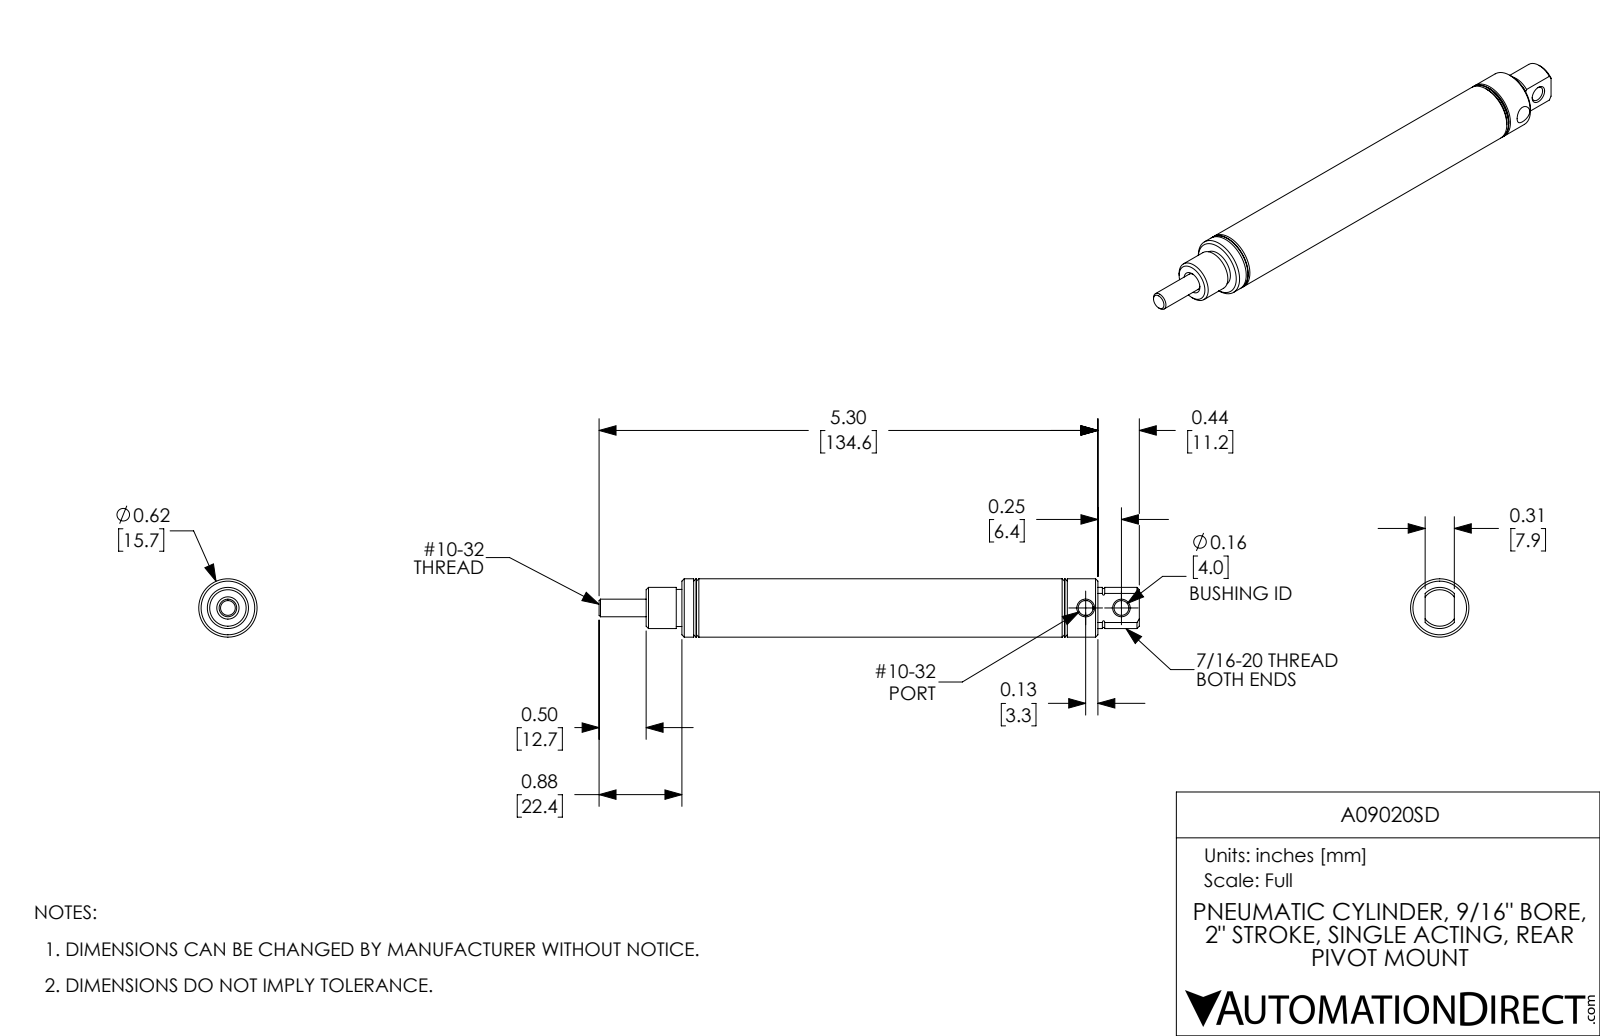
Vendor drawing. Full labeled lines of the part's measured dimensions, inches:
Part name (STEP PRODUCT): A09020SD-MainBody; A09020SD-Rod; A09020SD
STEP written by: SolidWorks 2017 (AUTOMOTIVE_DESIGN)
Units: inches
Bodies: 2 solids, 94 faces (19 planar, 38 cylindrical, 37 other)
Overall size (bounding box): 5.74 × 0.62 × 0.62
Volume: 0.981 in³ · Surface area: 20.42 in²
Round holes (diameter × count): ⌀0.156 ×1, ⌀0.157 ×1, ⌀0.159 ×1, ⌀0.187 ×1, ⌀0.19 ×1, ⌀0.563 ×1
Round bosses / shafts (diameter × count): ⌀0.62 ×1, ⌀0.437 ×1, ⌀0.394 ×1
Main face-to-face distances: 2.5, 0.5, 2, 3.46, 2.96, 0.96, 0.96, 1.46, 3.46, 4.42
Hole centre spacings: 0.38
